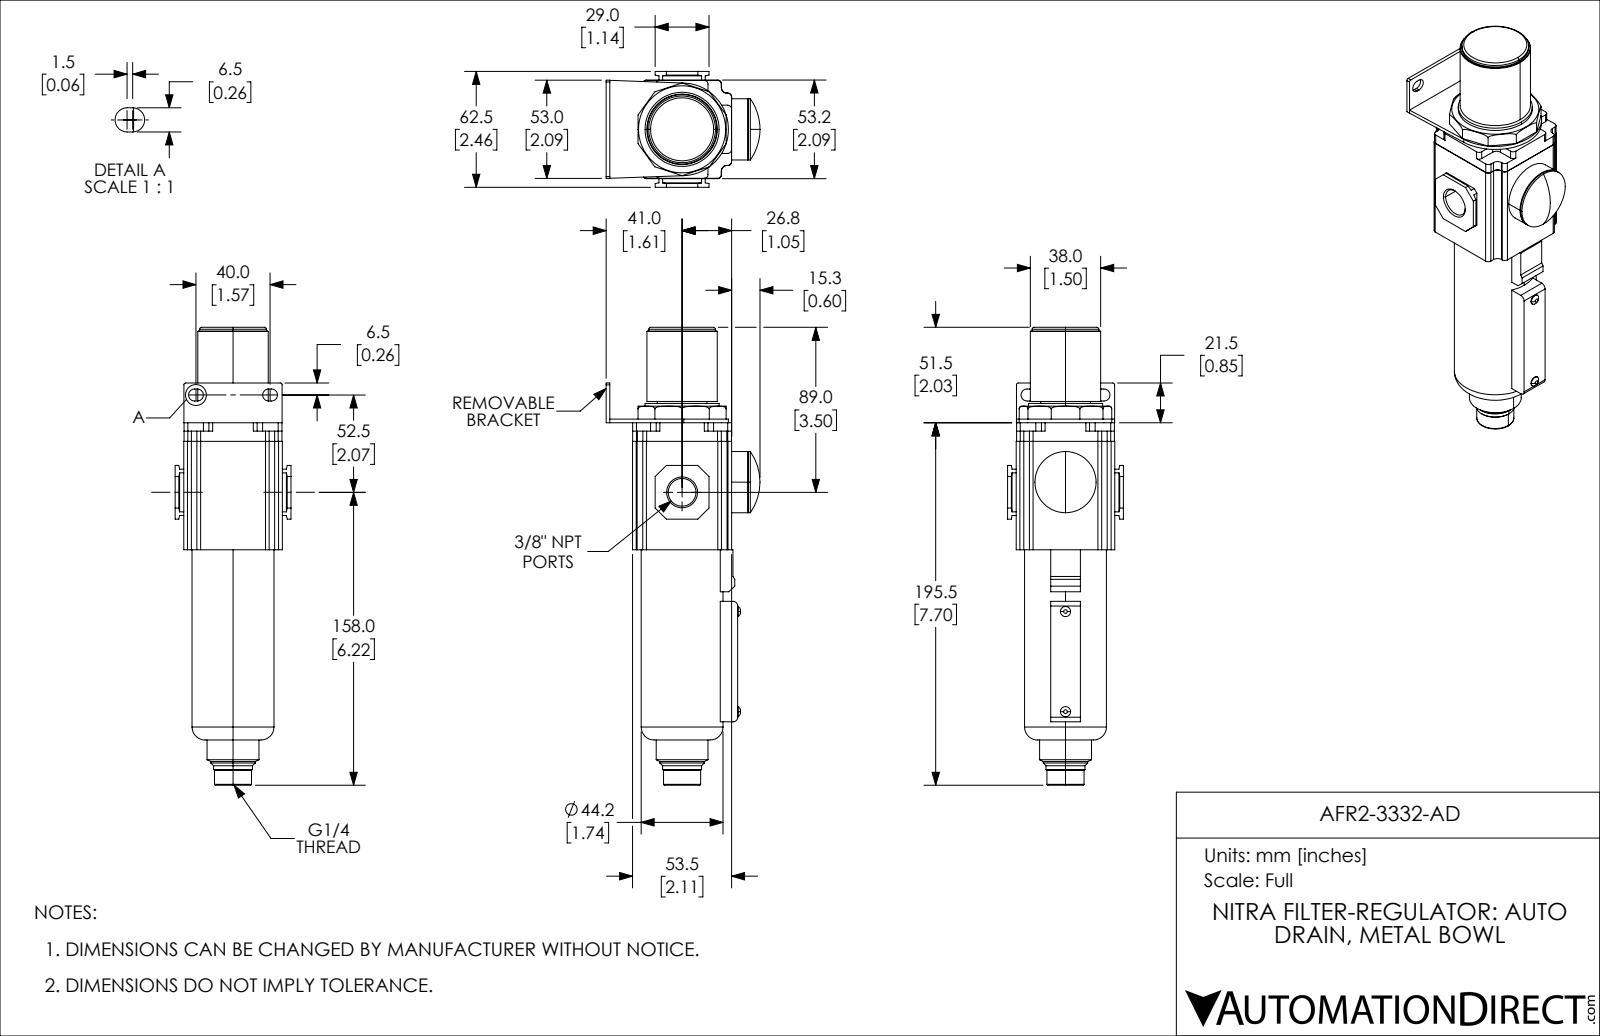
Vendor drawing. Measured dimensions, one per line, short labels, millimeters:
name: AFR2-3332-AD
written by: SolidWorks 2019 (CONFIG_CONTROL_DESIGN)
unit: mm
bodies: 1 solid, 235 faces (128 planar, 77 cylindrical, 30 other)
size: 247 × 83.03 × 62.5
volume: 438 897 mm³; area: 52 897 mm²
holes: 1× ⌀11.45, 1× ⌀14.95
bosses: 2× ⌀5.5, 1× ⌀44.2, 1× ⌀40, 1× ⌀38, 1× ⌀36, 1× ⌀33, 1× ⌀28, 1× ⌀26.78
rounds: 24× R2, 12× R3, 4× R3.25, 2× R1, 2× R2.5, 1× R25
face distances: 2, 53.2, 18.6, 34.6, 16, 53.5, 39.25, 14.25, 4.65, 23.25
